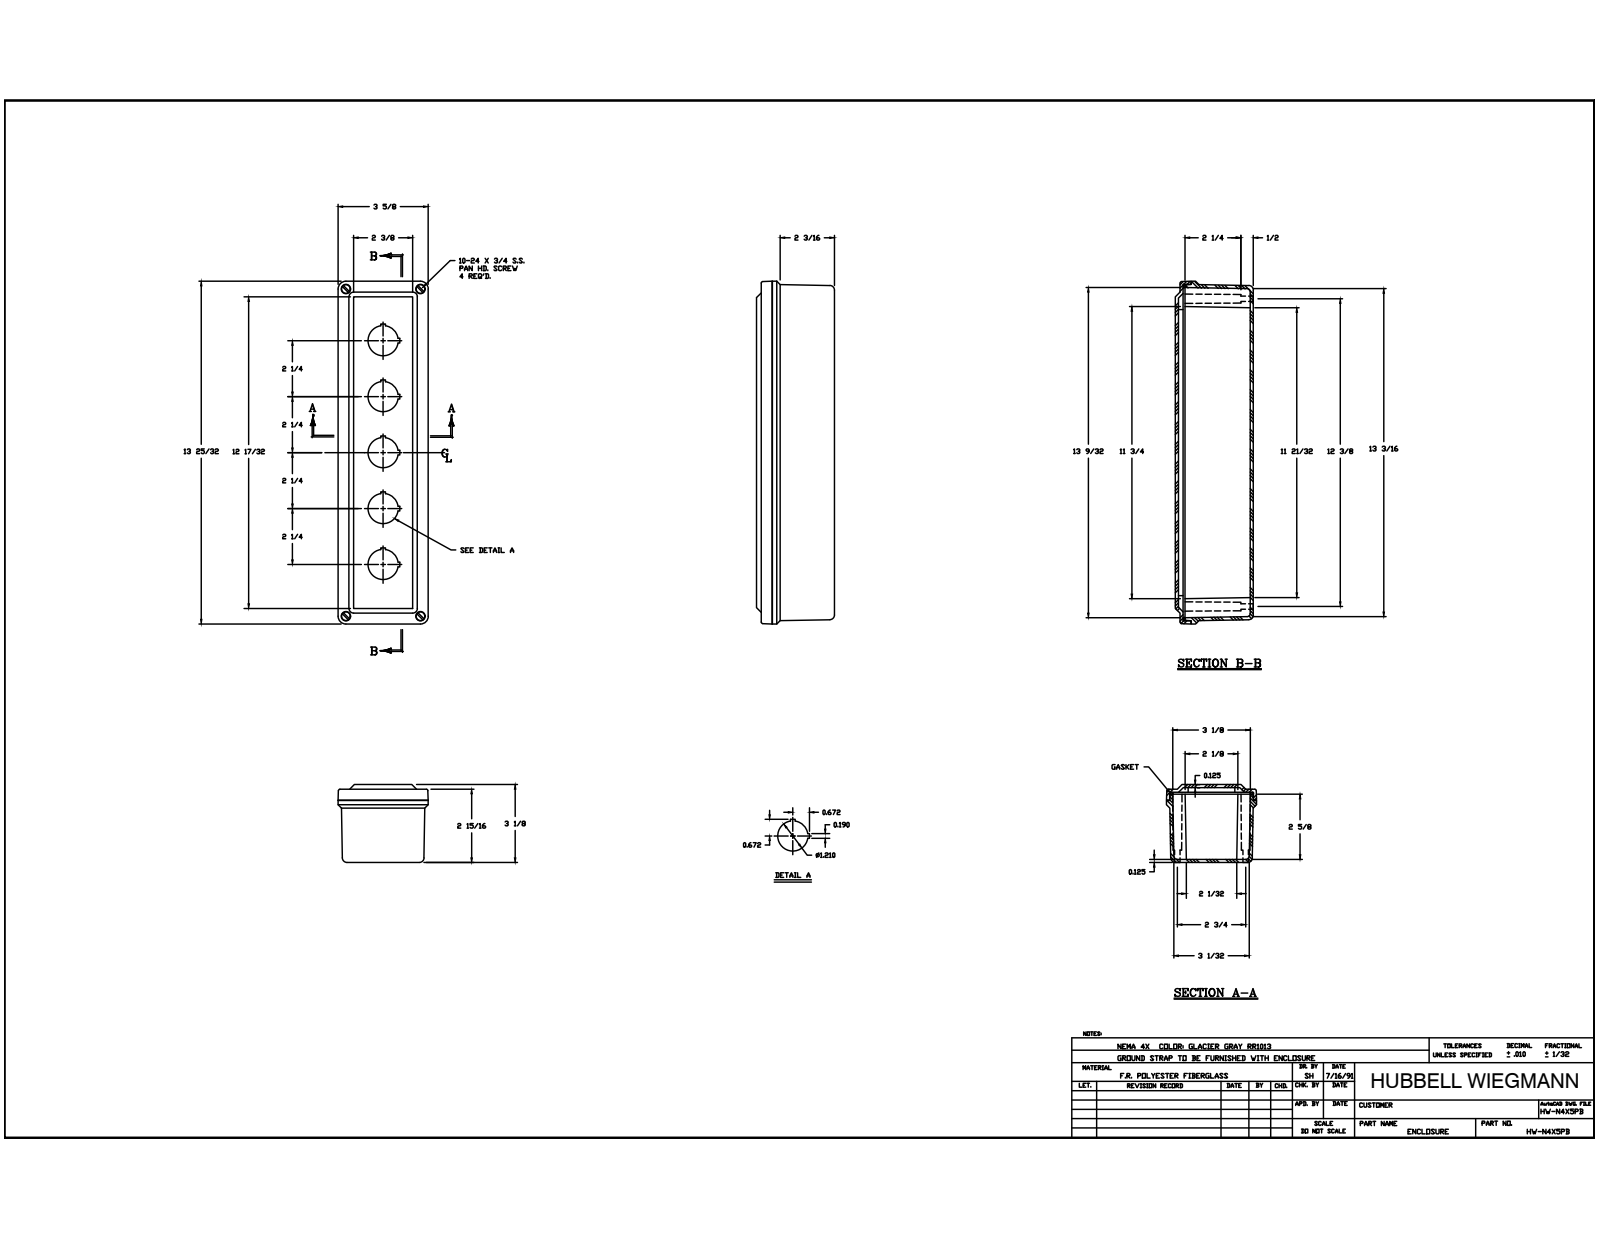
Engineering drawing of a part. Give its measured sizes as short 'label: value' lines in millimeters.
name: WPCF1432 BOX; 10-24 X 0.4375 DP BRASS INSERT; 10-24x0.75L combo screw; WPCF1432 GASKET (+3 more)
written by: Autodesk Inventor 2014 (AUTOMOTIVE_DESIGN)
unit: mm
bodies: 11 solids, 419 faces (201 planar, 126 cylindrical, 92 other)
size: 350.1 × 92.08 × 79.25
volume: 444 286 mm³; area: 266 662 mm²
holes: 8× ⌀5.56, 5× ⌀30.73, 4× ⌀3.68, 4× ⌀4.83, 4× ⌀9.52
bosses: 4× ⌀9.42, 4× ⌀5.54, 4× ⌀4.5
rounds: 20× R0.79, 16× R0.3, 8× R1.22, 8× R7.94, 4× R1.59, 4× R4.47, 4× R4.76, 4× R5.59
face distances: 3.18, 3.16, 76.07, 71.31, 4.76, 79.25, 7.94, 72.89, 3.17, 12.7
hole spacings: 10.42, 55.28, 57.15, 65.09, 73.69, 105.93, 116.35, 160.99
